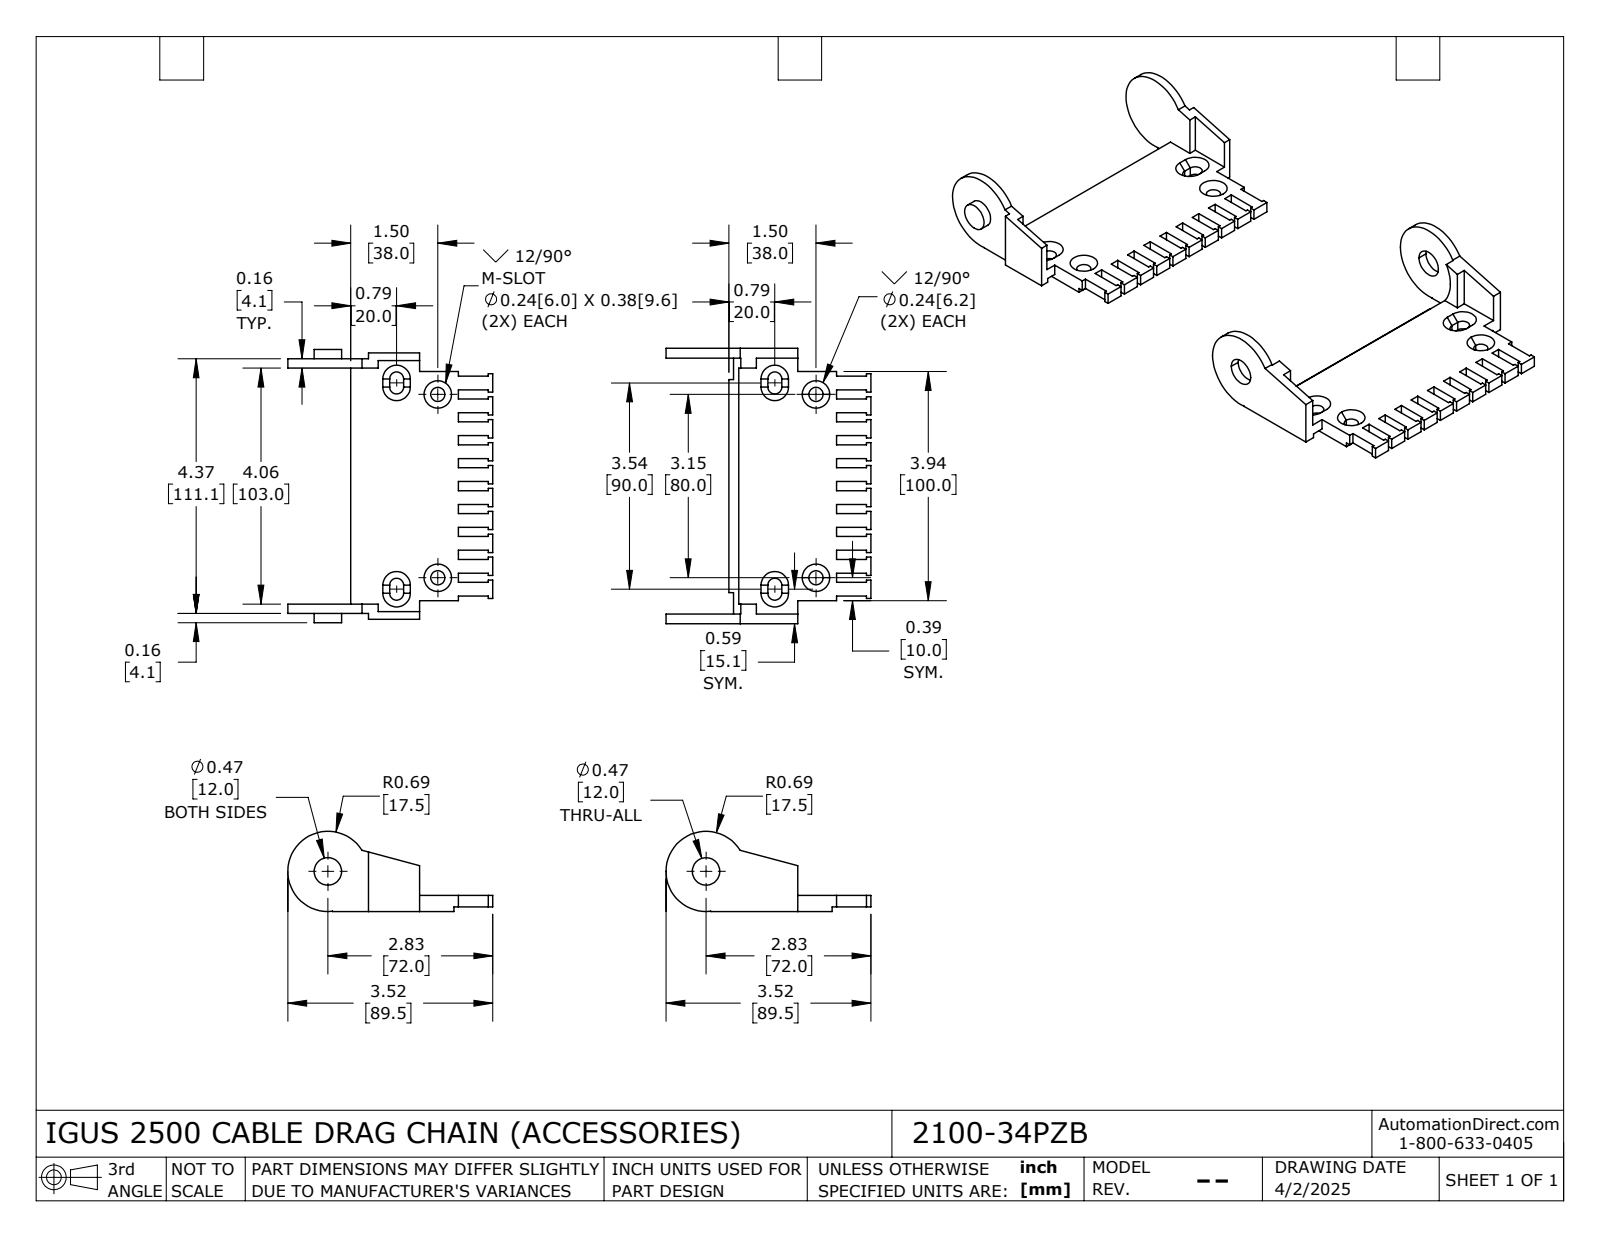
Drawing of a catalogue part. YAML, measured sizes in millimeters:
part_name: "2100-34PZB"
step_written_by: "SolidWorks 2024 (AUTOMOTIVE_DESIGN)"
units: millimeters
bodies: {solids: 2, faces: 291, planar: 248, cylindrical: 29, other: 14}
overall_size: [254.6, 120.2, 35]
volume: 99966
surface_area: 47382
round_holes:
  - {diameter: 6.2, count: 4}
  - {diameter: 12, count: 1}
round_bosses_or_shafts:
  - {diameter: 12, count: 1}
partial_cylinders:
  - {radius: 3.05, count: 8}
  - {radius: 17.5, count: 2}
  - {radius: 17.7, count: 1}
face_to_face_distances: [7, 2, 4.3, 111.6, 5, 8.6, 115.9, 107.3, 4.55, 115.65]
hole_center_spacings: [80, 165.1, 183.46]
